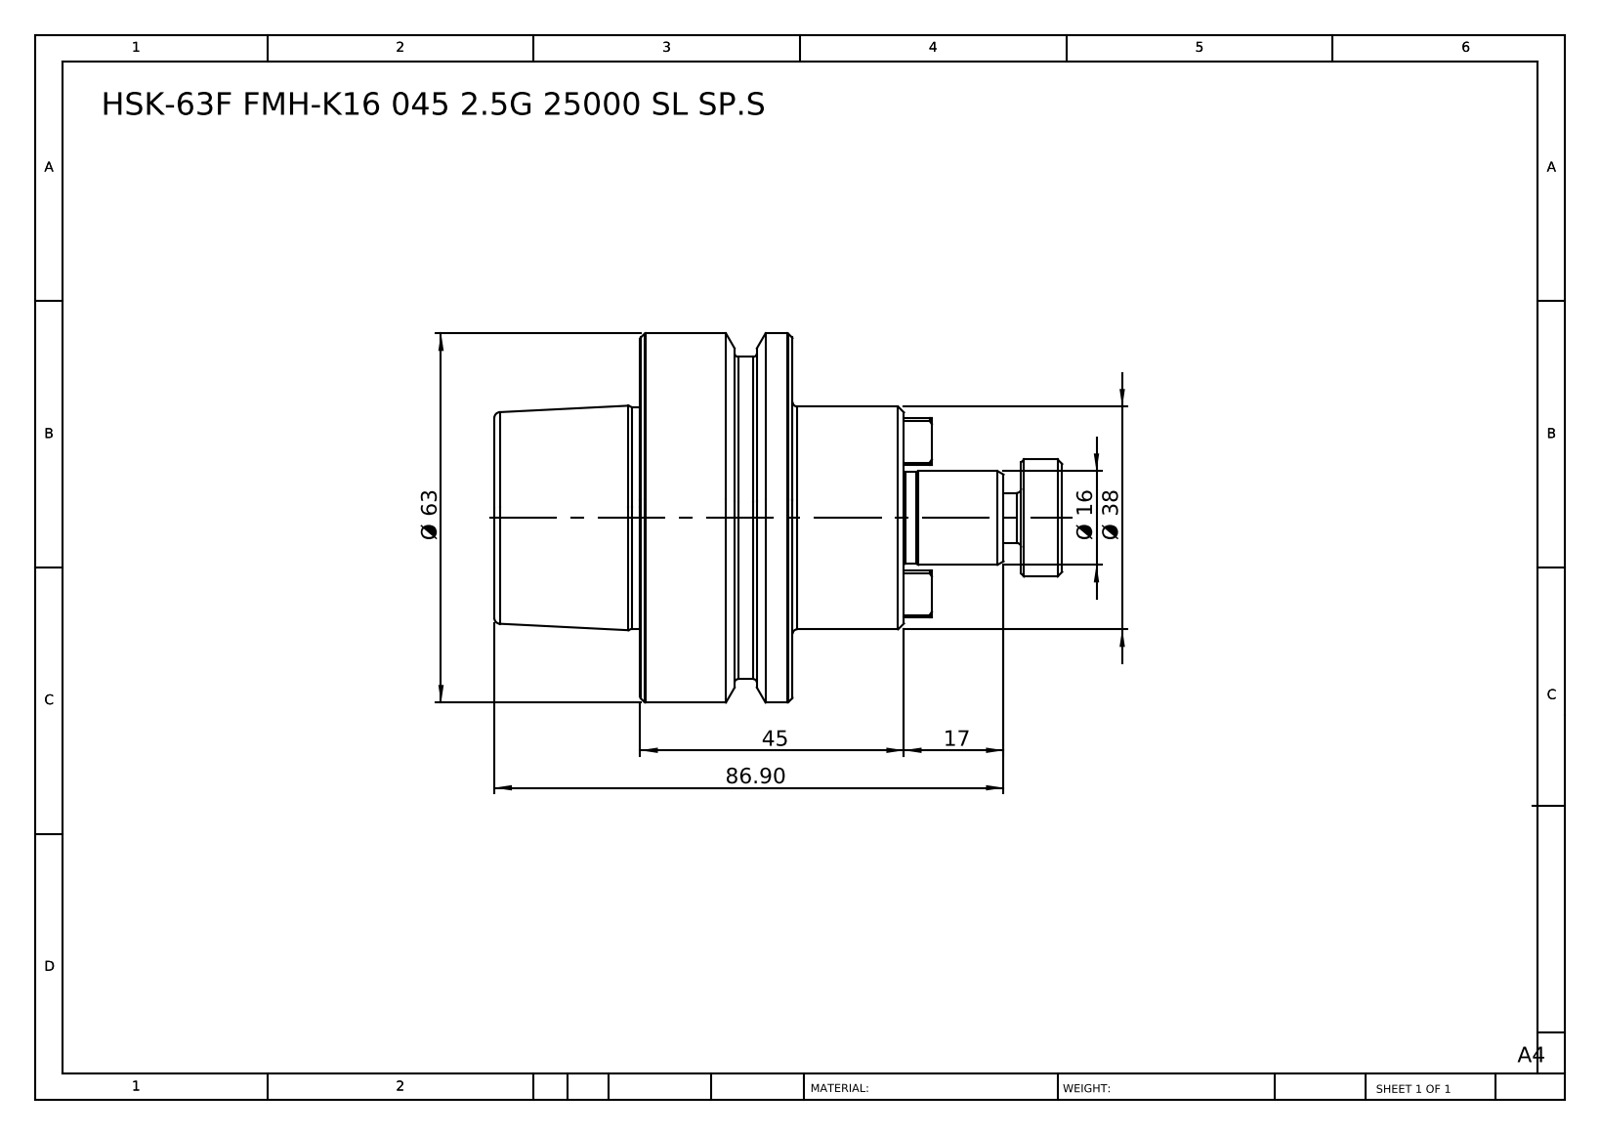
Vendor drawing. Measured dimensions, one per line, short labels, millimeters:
name: HSK-63F FMH-K16 045 2.5G 25000 SL SP
written by: SolidWorks 2014 (CONFIG_CONTROL_DESIGN)
unit: mm
bodies: 2 solids, 104 faces (38 planar, 18 cylindrical, 48 other)
size: 96.9 × 63 × 63
volume: 132 278 mm³; area: 21 568 mm²
bosses: 1× ⌀63, 1× ⌀55, 1× ⌀38, 1× ⌀37.8, 1× ⌀20, 1× ⌀16, 1× ⌀15.6, 1× ⌀8.5
face distances: 26, 50.9, 24.9, 19, 45, 69.9, 27, 46, 72, 96.9
